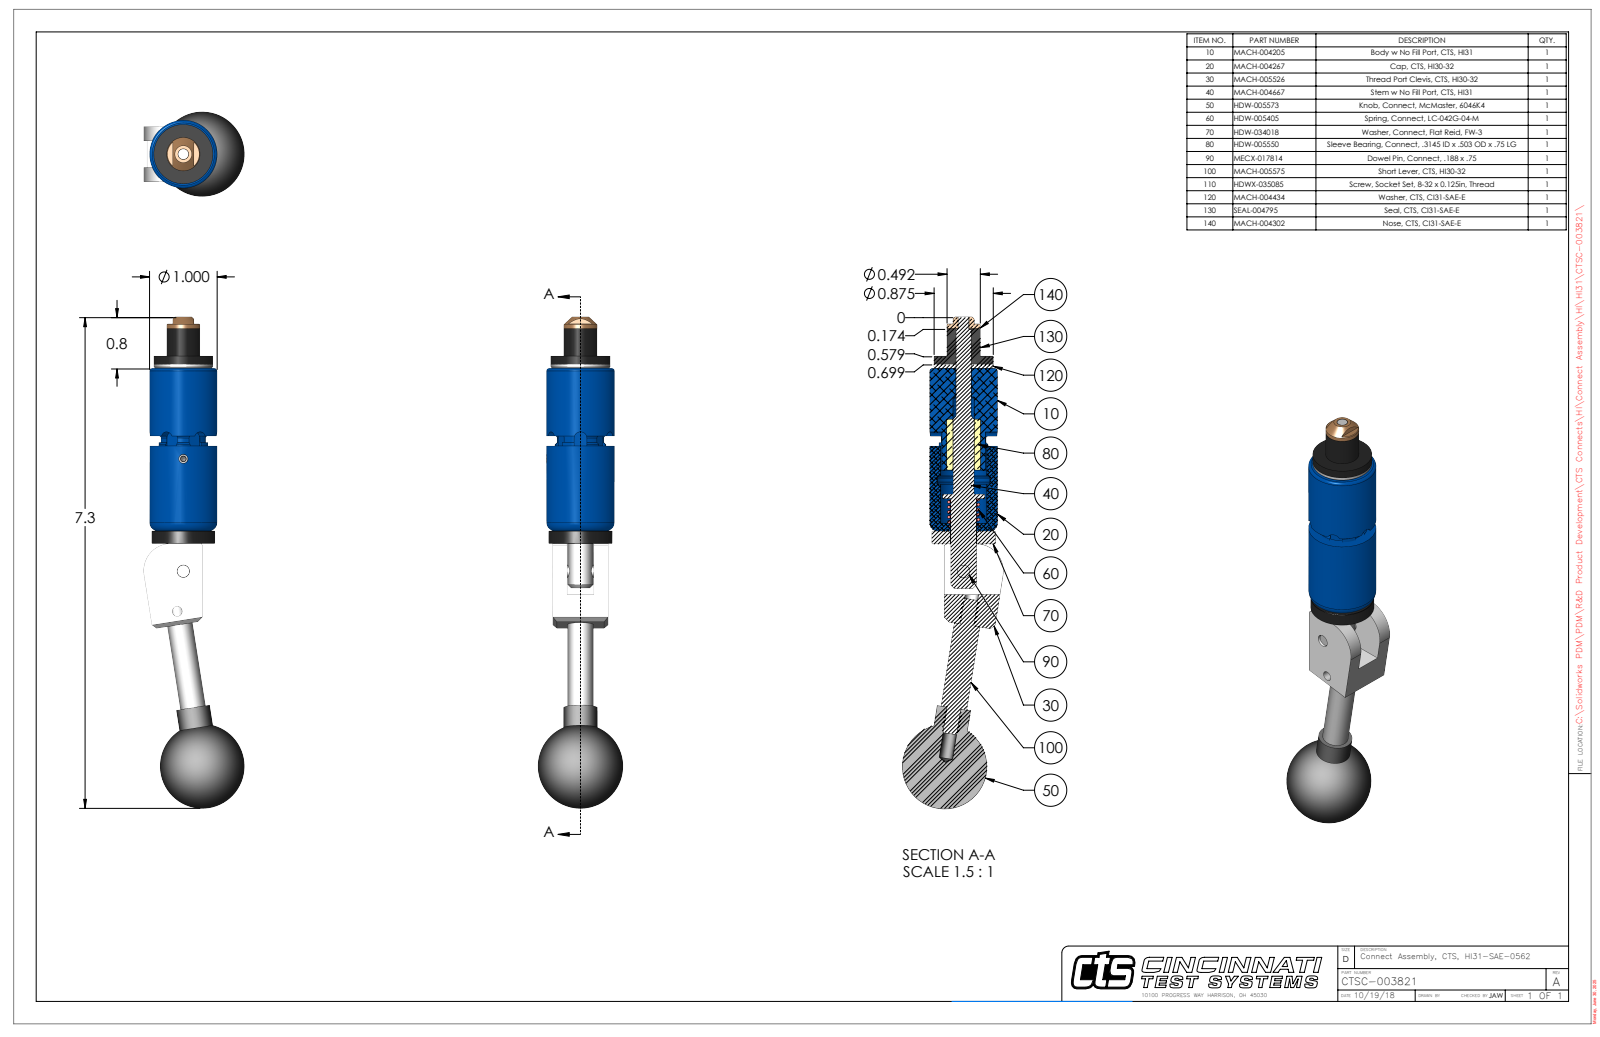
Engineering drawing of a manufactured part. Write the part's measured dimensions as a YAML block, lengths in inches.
part_name: "CTSC-003821"
step_written_by: "SolidWorks 2023 (AUTOMOTIVE_DESIGN)"
units: inches
bodies: {solids: 9, faces: 277, planar: 107, cylindrical: 110, other: 60}
overall_size: [7.256, 1.492, 1.25]
volume: 3.949
surface_area: 32.91
round_holes:
  - {diameter: 0.201, count: 2}
  - {diameter: 0.136, count: 1}
  - {diameter: 0.15, count: 1}
  - {diameter: 0.159, count: 1}
  - {diameter: 0.189, count: 1}
  - {diameter: 0.218, count: 1}
  - {diameter: 0.228, count: 1}
  - {diameter: 0.229, count: 1}
  - {diameter: 0.385, count: 1}
  - {diameter: 0.392, count: 1}
  - {diameter: 0.688, count: 1}
round_bosses_or_shafts:
  - {diameter: 1, count: 1}
  - {diameter: 0.936, count: 1}
  - {diameter: 0.875, count: 1}
  - {diameter: 0.875, count: 1}
  - {diameter: 0.5, count: 1}
  - {diameter: 0.492, count: 1}
  - {diameter: 0.38, count: 1}
  - {diameter: 0.375, count: 1}
partial_cylinders:
  - {radius: 0.093, count: 6}
  - {radius: 0.029, count: 2}
  - {radius: 0.375, count: 1}
  - {radius: 0.4, count: 1}
  - {radius: 0.448, count: 1}
face_to_face_distances: [0.21, 0.602, 0.06, 2.46, 2.4, 0.812, 2.647, 2.587, 0.187, 0.391]
hole_center_spacings: [0.599, 1.658, 2.252]
